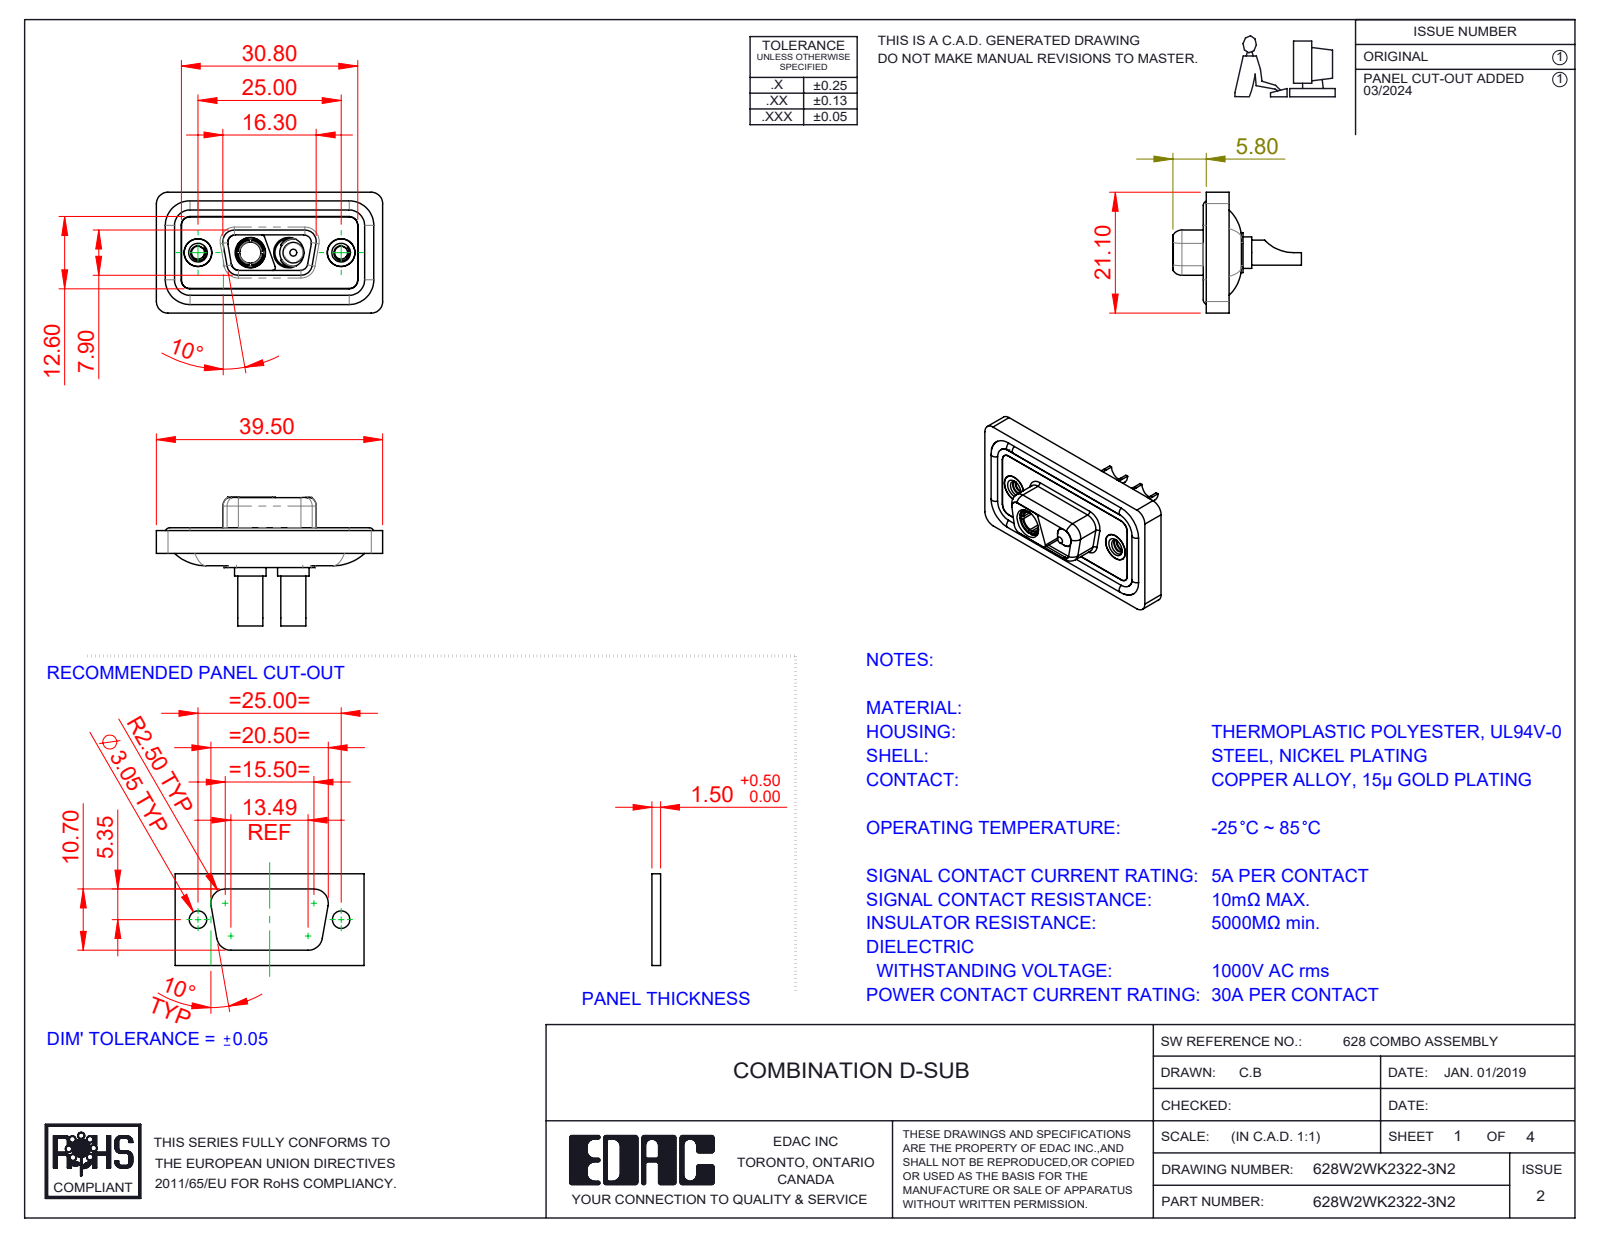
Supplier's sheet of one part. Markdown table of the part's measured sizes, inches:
| quantity | value |
| --- | --- |
| part name | Power Pin_30A SC; 628Combo Housing_2WK2; 628Combo Shell Rear_09 Contacts; 628Combo Threaded Rivet_2 (+4 more) |
| STEP written by | SolidWorks 2023 (CONFIG_CONTROL_DESIGN) |
| units | inches |
| bodies | 11 solids, 512 faces (150 planar, 237 cylindrical, 125 other) |
| overall size | 1.555 × 0.884 × 0.831 |
| volume | 0.284 in³ |
| surface area | 11.72 in² |
| round holes (diameter × count) | 0.191 × 4, 0.089 × 2, 0.138 × 2, 0.157 × 2, 0.159 × 2, 0.197 × 2, 0.209 × 2, 0.146 × 1 |
| round bosses / shafts (diameter × count) | 0.063 × 4, 0.217 × 2, 0.205 × 2, 0.195 × 2, 0.189 × 2, 0.187 × 2, 0.173 × 2, 0.148 × 2 |
| partial cylindrical surfaces (radius × count) | 0.059 × 22, 0.079 × 18, 0.053 × 8, 0.063 × 8, 0.02 × 6, 0.01 × 4, 0.024 × 4, 0.026 × 4 |
| main face-to-face distances | 0.016, 0.043, 0.114, 0.063, 0.02, 0.071, 0.222, 0.211, 0.122, 0.028 |
| hole center spacings | 0.36, 0.624, 0.265, 0.984 |
